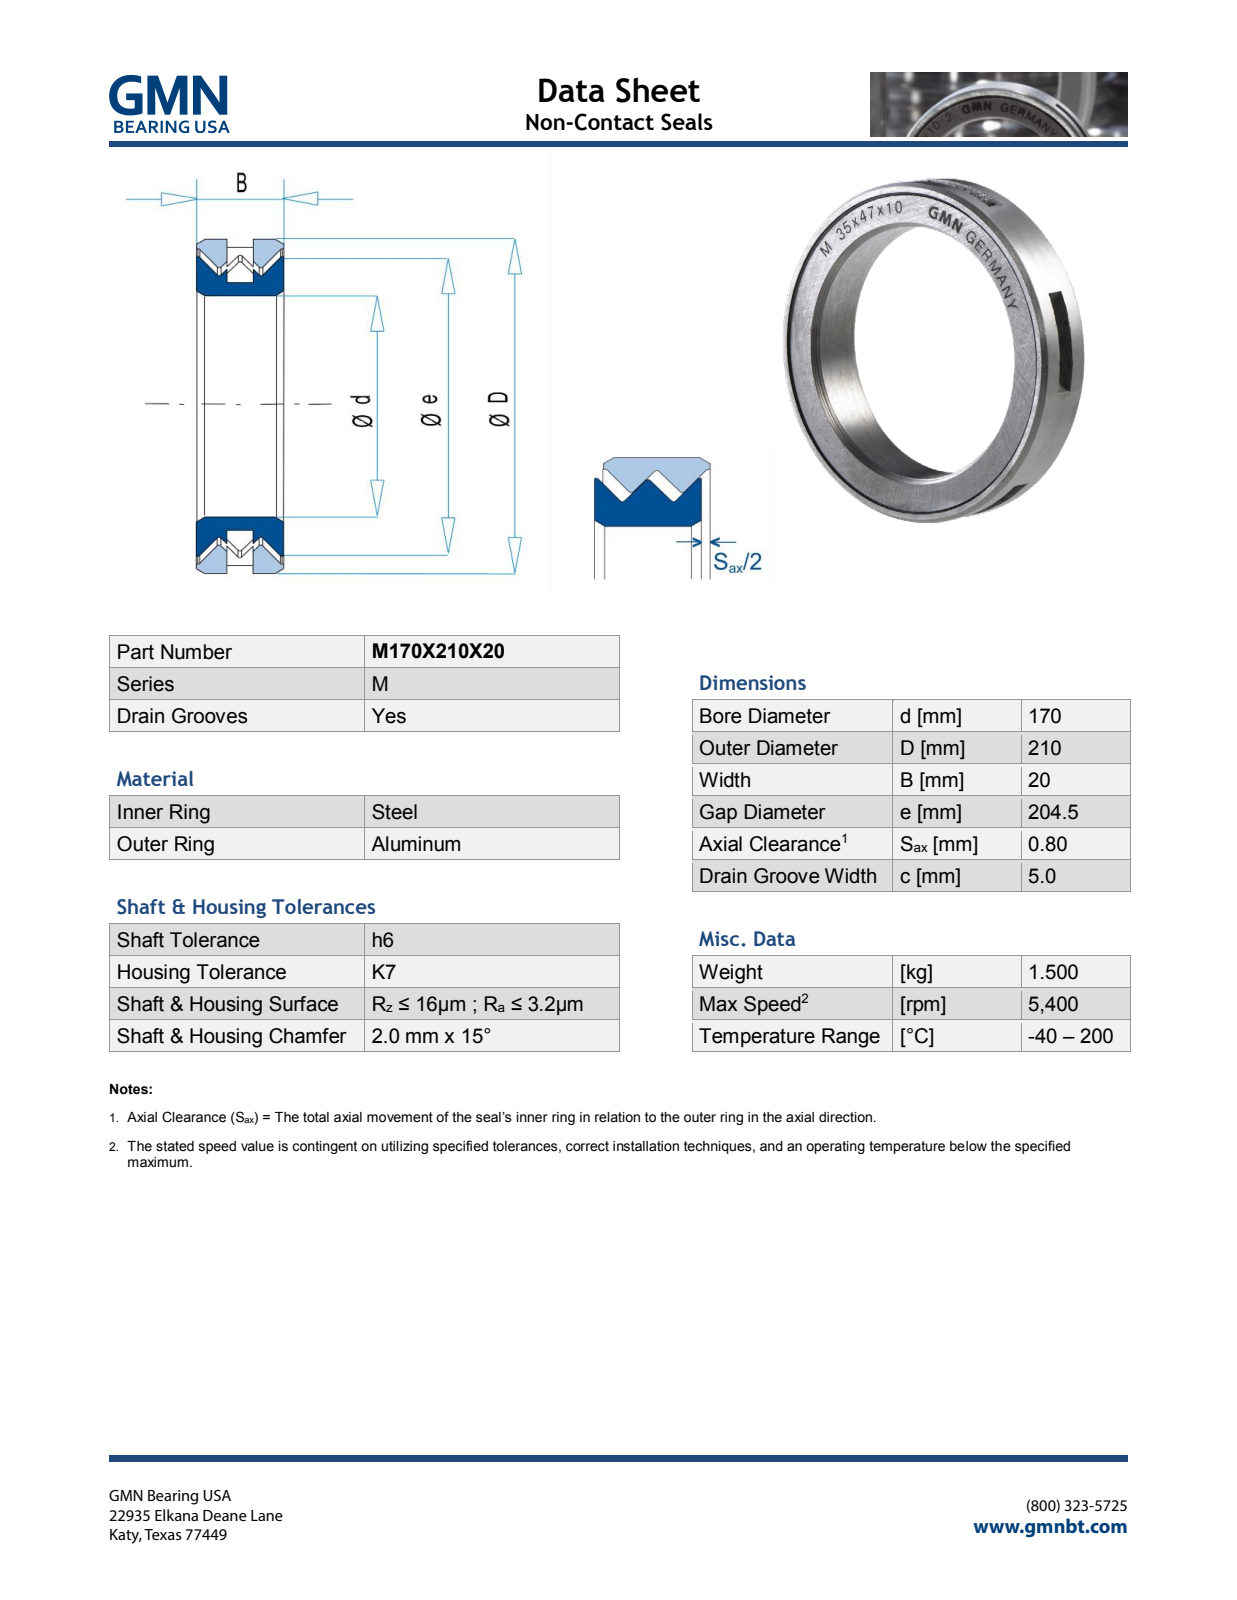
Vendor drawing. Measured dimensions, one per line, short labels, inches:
name: M170X210X20_PRT
written by: PRO/ENGINEER BY PARAMETRIC TECHNOLOGY CORPORATION, 2013150 (AUTOMOTIVE_DESIGN)
unit: in
bodies: 1 solid, 711 faces (580 planar, 41 cylindrical, 90 other)
size: 8.268 × 8.268 × 0.791
volume: 13.74 in³; area: 122.4 in²
holes: 1× ⌀6.693, 1× ⌀8.028
bosses: 1× ⌀8.268
rounds: 11× R0.394
face distances: 0.787, 0.295, 0.492, 0.791, 0.298, 0.495, 0.197, 0.069, 0.555, 0.485
